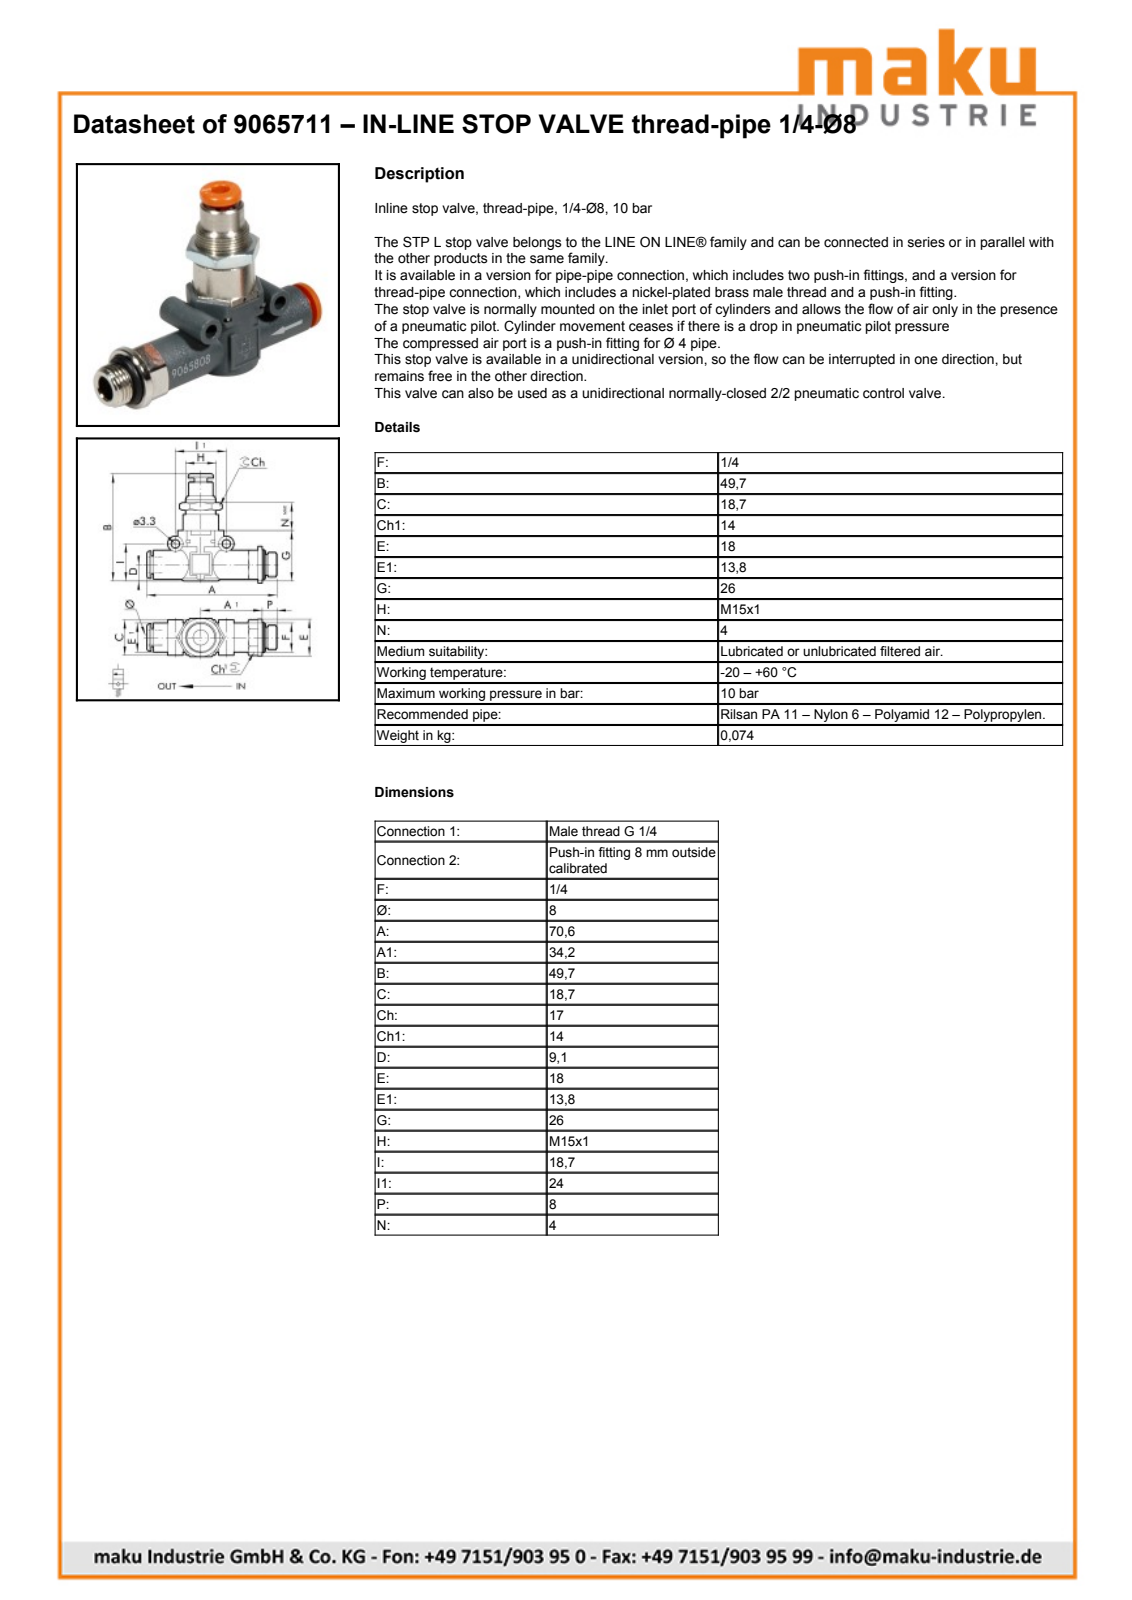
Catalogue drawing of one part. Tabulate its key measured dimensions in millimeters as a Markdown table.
| quantity | value |
| --- | --- |
| part name | 9065711; LINE-ON-LINE D8 PNV_L-body; LINE-ON-LINE D8-1/4 RML-thread port; LINE-ON-LINE D8 VNR-L bushing (+2 more) |
| STEP written by | PARTsolutions (AUTOMOTIVE_DESIGN) |
| units | millimeters |
| bodies | 5 solids, 186 faces (111 planar, 59 cylindrical, 16 other) |
| overall size | 70.6 × 49.7 × 18.7 |
| volume | 13 655 mm³ |
| surface area | 11 637 mm² |
| round holes (diameter × count) | 3.3 × 2, 6 × 2, 4.5 × 1, 5.53 × 1, 6.2 × 1, 8 × 1, 8.1 × 1, 11 × 1, 11.65 × 1, 12.5 × 1, 15 × 1 |
| round bosses / shafts (diameter × count) | 18 × 2, 7.2 × 2, 6 × 2, 18.8 × 1, 13.8 × 1, 13.6 × 1, 13.16 × 1, 12.8 × 1 |
| partial cylindrical surfaces (radius × count) | 3.75 × 1, 7.95 × 1, 10.35 × 1, 11.45 × 1 |
| main face-to-face distances | 24.1, 23, 4.1, 20, 18.5, 20.5, 2, 47.1, 43, 22 |
| hole center spacings | 15.37, 24 |
